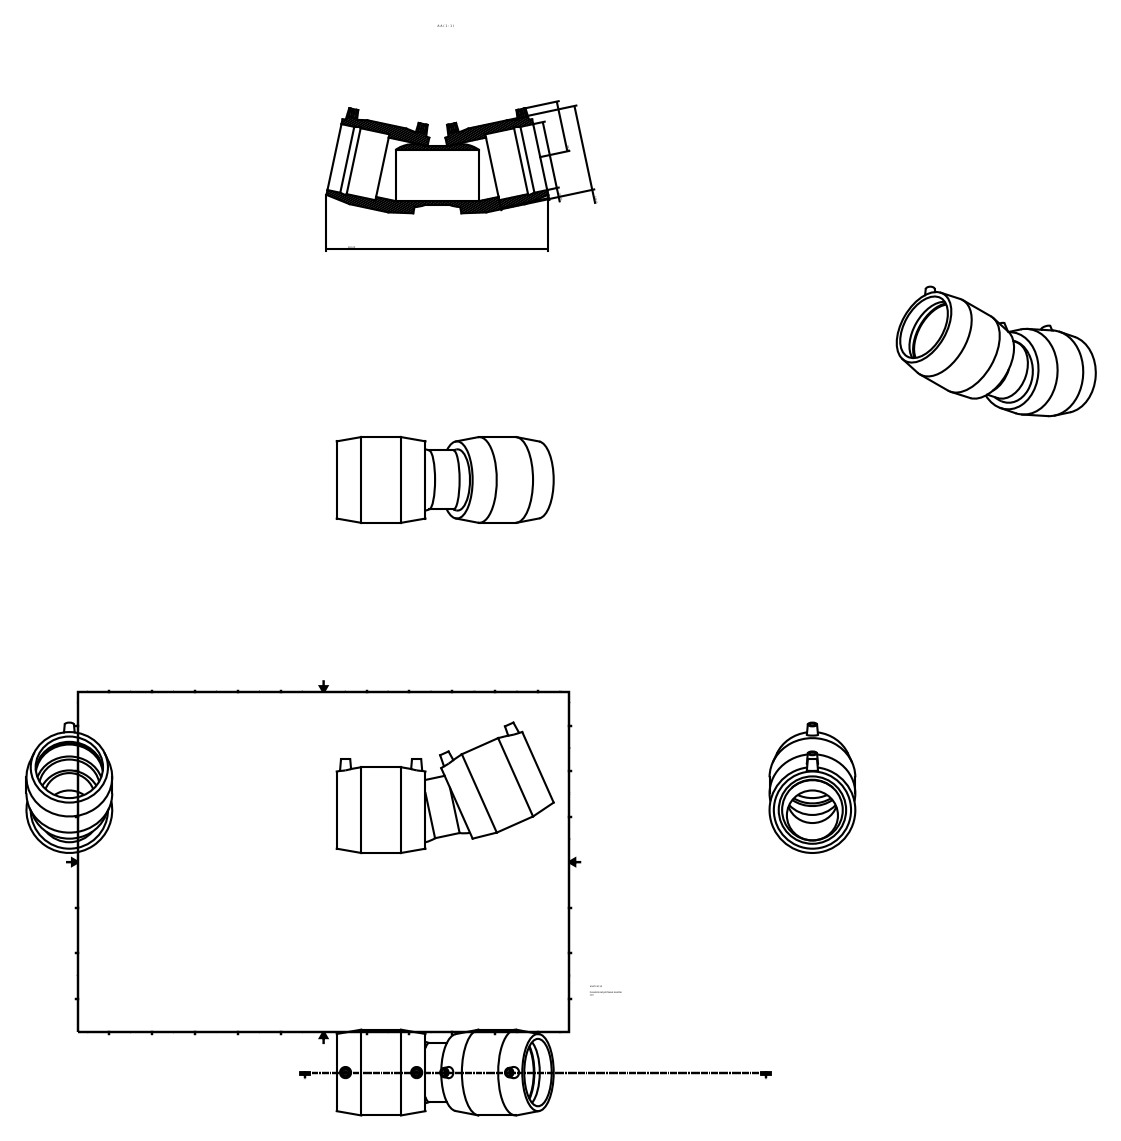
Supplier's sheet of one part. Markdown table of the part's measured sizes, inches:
| quantity | value |
| --- | --- |
| part name | 4947C4110 |
| STEP written by | Autodesk Inventor 2015 (AUTOMOTIVE_DESIGN) |
| units | inches |
| bodies | 1 solid, 50 faces (20 planar, 18 cylindrical, 12 other) |
| overall size | 13.941 × 8.378 × 5.512 |
| volume | 119.1 in³ |
| surface area | 466.1 in² |
| round holes (diameter × count) | 0.394 × 4, 4.331 × 3, 3.898 × 2, 3.282 × 1 |
| round bosses / shafts (diameter × count) | 0.157 × 4, 5.512 × 2, 3.792 × 1 |
| main face-to-face distances | 5.701, 5.704, 3.15, 2.551, 2.552, 3.151, 1.26, 1.89, 4.441, 4.443 |
| hole center spacings | 4.561 |
